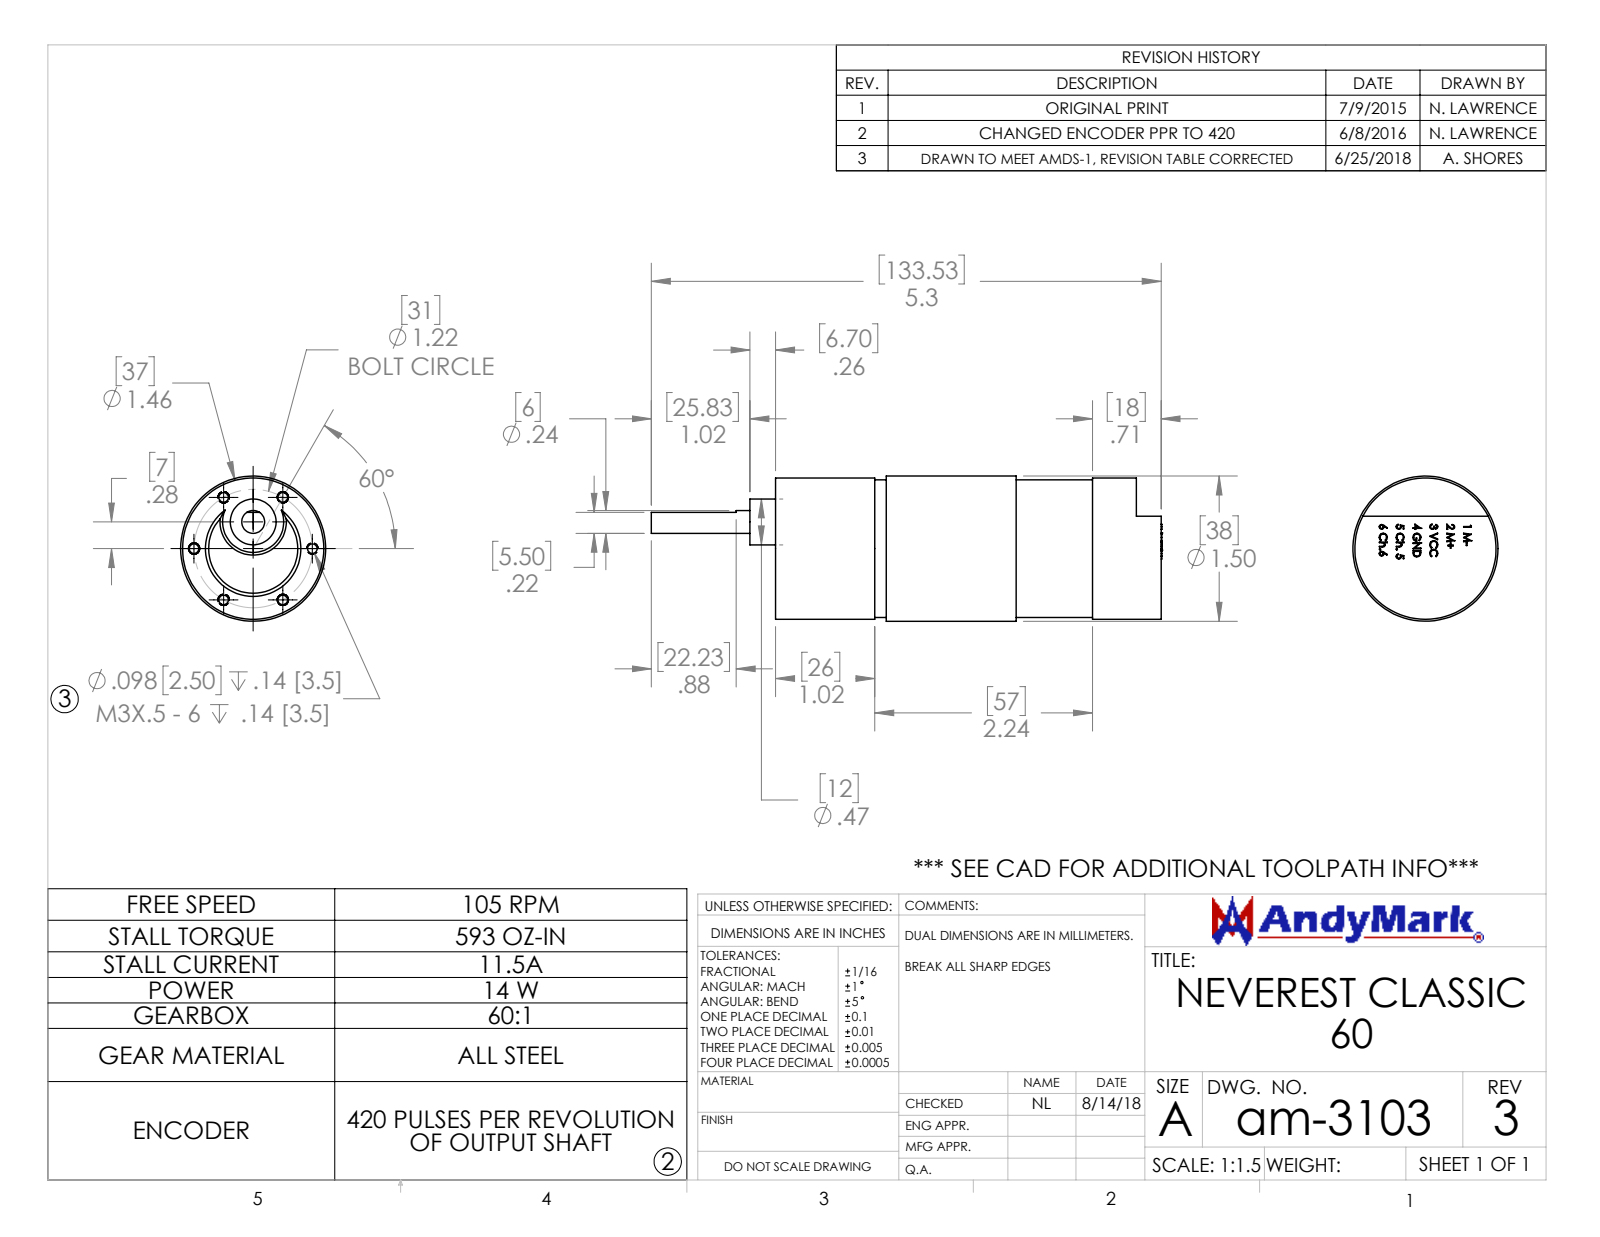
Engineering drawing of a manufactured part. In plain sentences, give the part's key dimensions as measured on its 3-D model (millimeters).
The part is named "am-3103 NeverRest Classic 60". Its 3-D file was written by "SolidWorks 2021 (AUTOMOTIVE_DESIGN)". It is 1 solid with 344 faces: 186 planar, 26 cylindrical and 132 other. Overall it measures 133.72 by 38 by 38 millimeters. Its volume is 108 922 cubic millimeters and its surface area 15 188 square millimeters. Round holes: 6 of diameter 2.5. Round bosses or shafts: 1 of diameter 38, 1 of diameter 37, 1 of diameter 36, 1 of diameter 12, 1 of diameter 6. The main face-to-face distances are 101, 0.7, 100.3, 6.5, 93.8, 94.5, 38, 72, 31.5, 65.5. The hole center spacings are 15.5, 26.85, 26.84, 30.99, 31.
